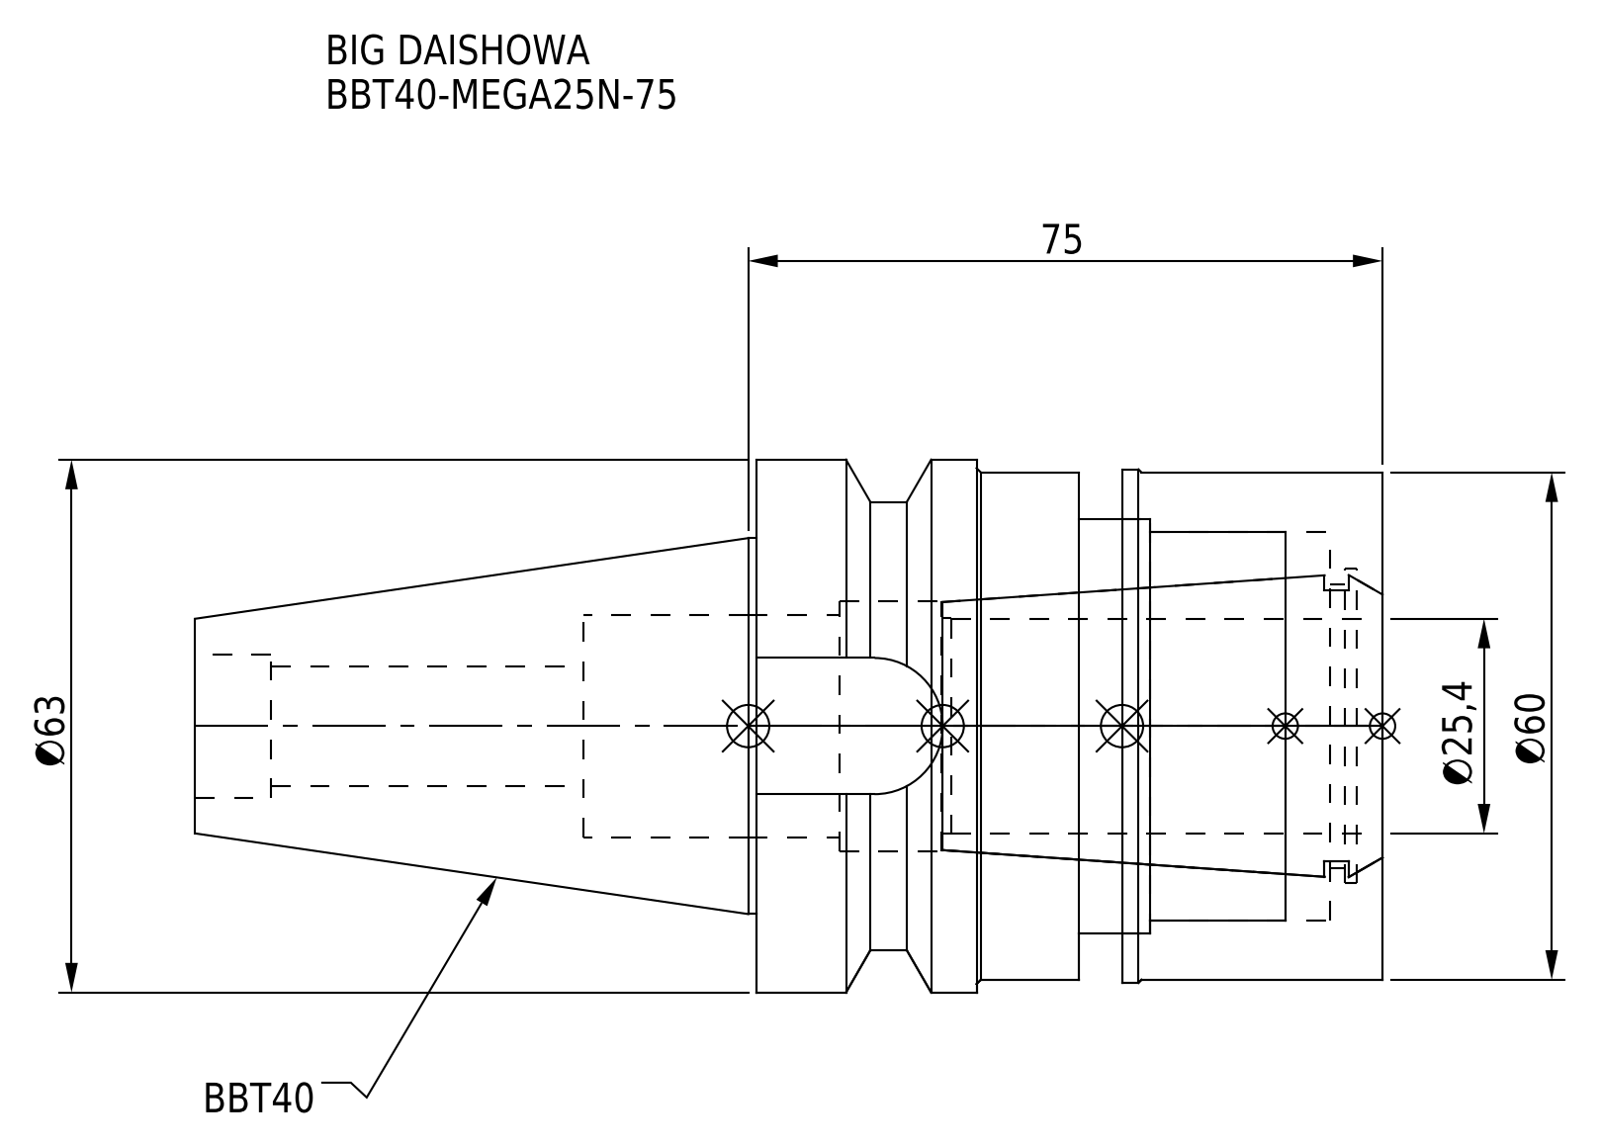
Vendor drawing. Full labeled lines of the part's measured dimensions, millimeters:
Part name (STEP PRODUCT): BBT40MN25075-254_ASM.stp; BBT40-MEGA25N-75-254-FreeParts; BBT40-MEGA25N-75-254.stp; DXF_TEMP_ASSY_ASM_4_ASM.stp (+3 more)
STEP written by: SolidWorks 2019 (CONFIG_CONTROL_DESIGN)
Units: millimetres
Bodies: 2 solids, 74 faces (22 planar, 38 cylindrical, 14 other)
Overall size (bounding box): 140.4 × 63 × 63
Volume: 186 451 mm³ · Surface area: 48 503 mm²
Round holes (diameter × count): ⌀14.2 ×1, ⌀17 ×1, ⌀26.3 ×1, ⌀26.31 ×1, ⌀29.6 ×1, ⌀33.5 ×1, ⌀37.2 ×1, ⌀46 ×1, ⌀49 ×1
Round bosses / shafts (diameter × count): ⌀63 ×1, ⌀60.7 ×1, ⌀60 ×1, ⌀53 ×1, ⌀44.45 ×1
Partial cylindrical surfaces — rounded edges, fillets, slot ends (radius × count): R8.05 ×1
Main face-to-face distances: 74, 30.8, 43.2, 35.9, 5.1, 38.1, 6.2, 24.6, 29.7, 67.8
